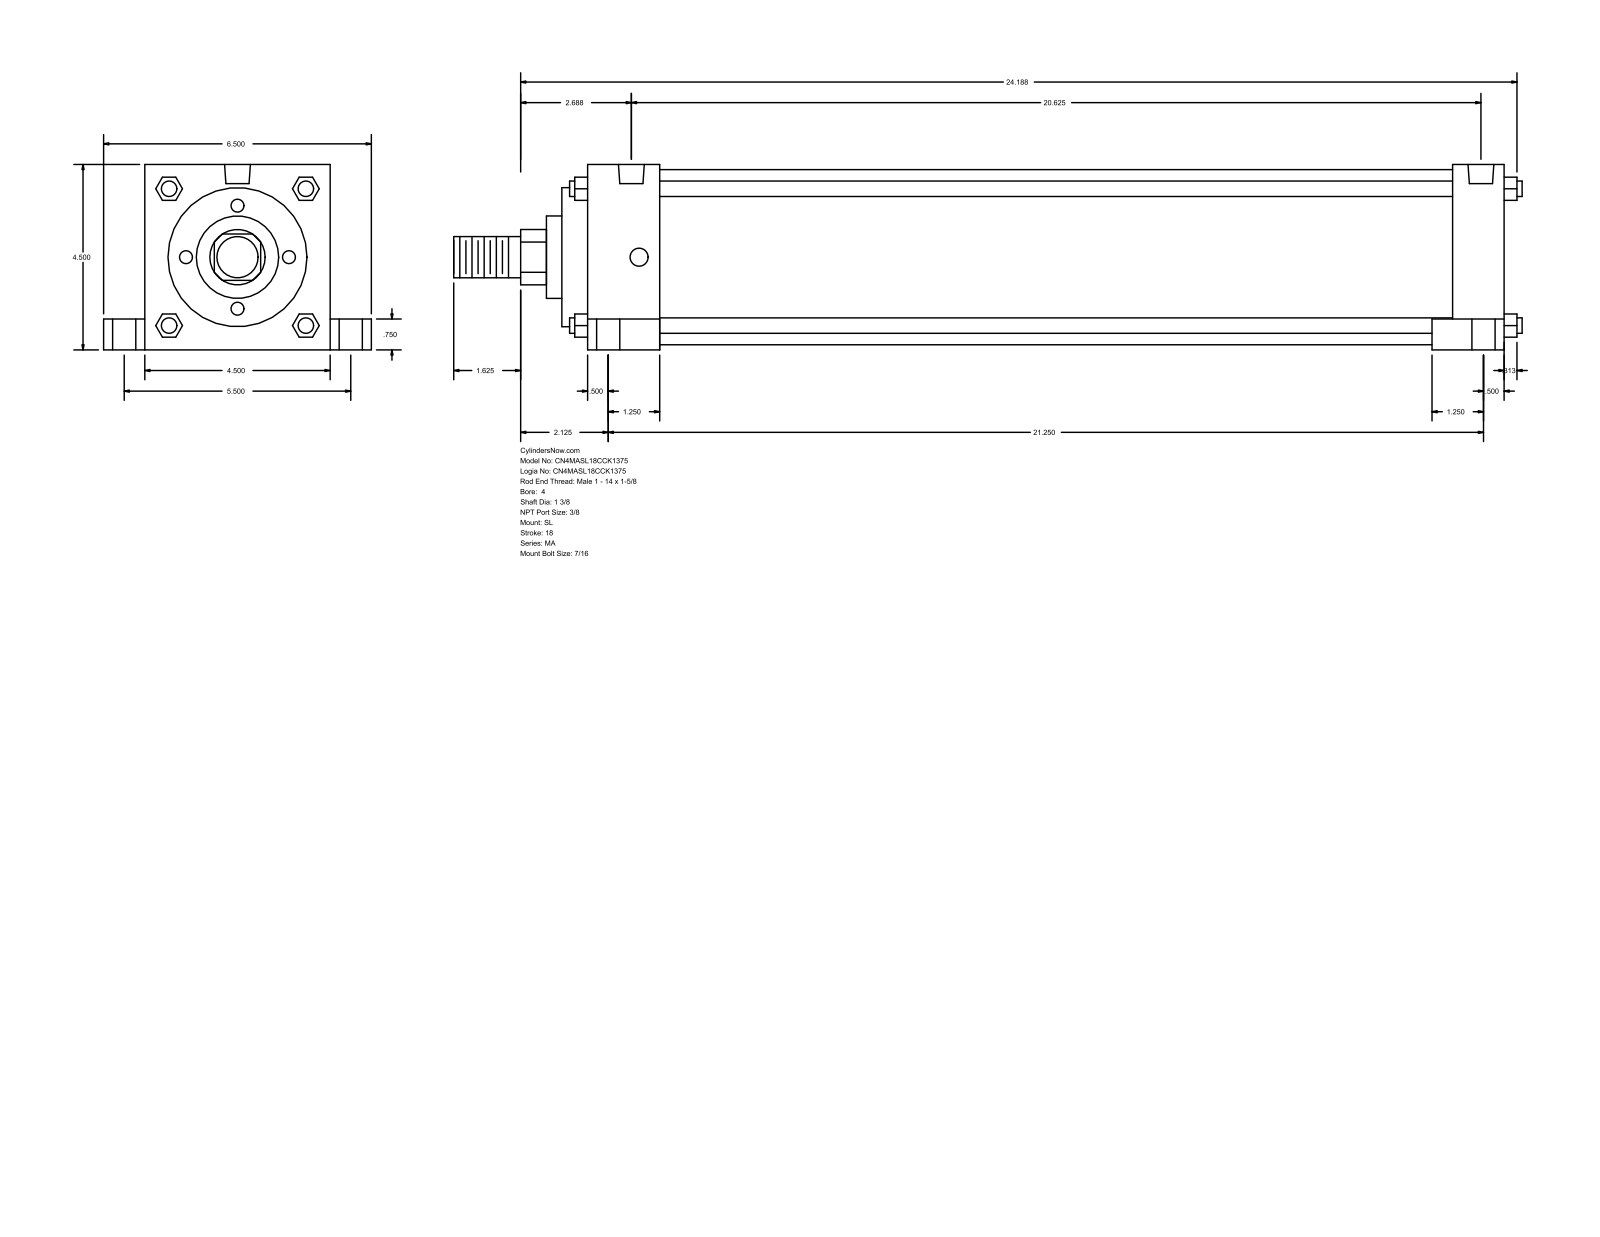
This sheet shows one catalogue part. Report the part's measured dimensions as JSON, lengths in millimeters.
{"part_name": "MA_SL__0400_1.375", "step_written_by": "GSSL Pune (CONFIG_CONTROL_DESIGN)", "units": "millimeters", "bodies": {"solids": 0, "faces": 150, "planar": 113, "cylindrical": 37, "other": 0}, "overall_size": [658.81, 165.1, 114.3], "round_holes": [[11.11, 4], [14.29, 4], [20.64, 4], [15.93, 2]], "round_bosses_or_shafts": [[9.53, 4], [107.95, 1], [85.72, 1], [50.8, 1], [34.92, 1], [25.4, 1]], "partial_cylinders_radius": [[17.06, 1]], "face_to_face_distances": [114.3, 565.15, 488.95, 581.02, 15.87, 60.32, 44.45, 520.7, 549.27, 533.4], "hole_center_spacings": [69.87, 70.14, 71.29, 72.4, 139.7, 514.35, 525.36, 530.09]}
